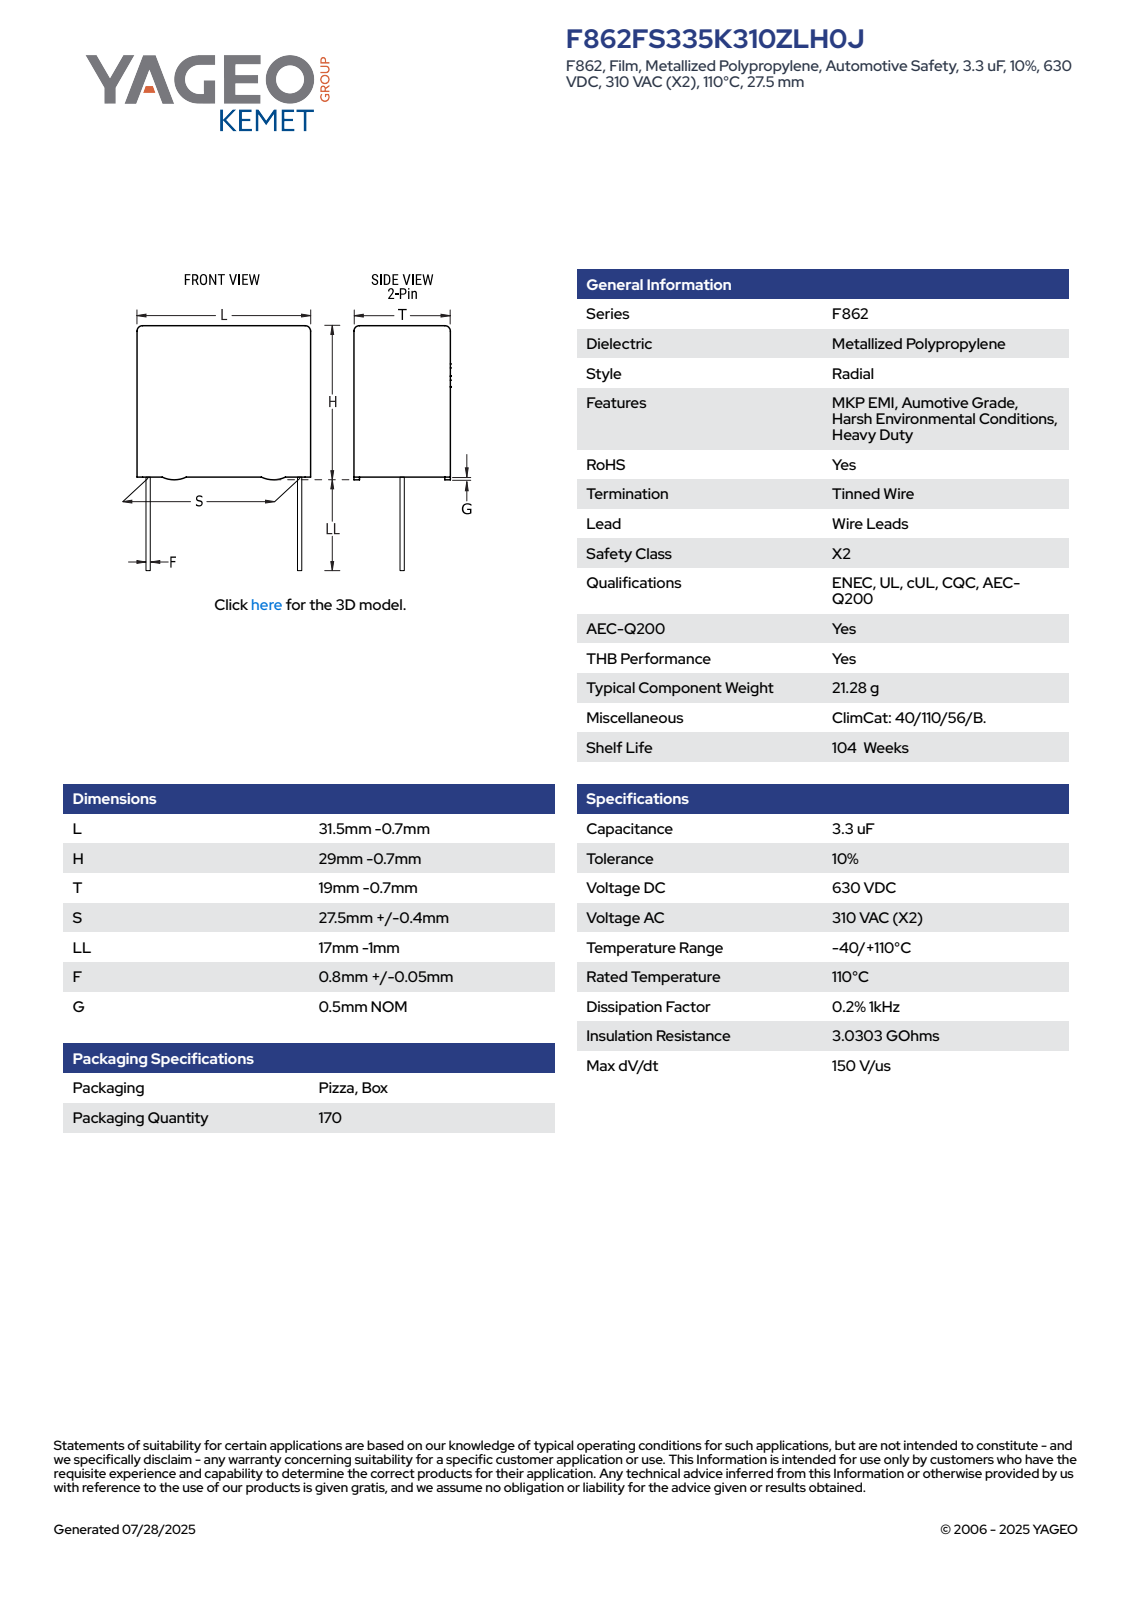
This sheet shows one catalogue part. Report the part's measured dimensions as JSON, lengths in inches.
{"part_name": "CFR_RBG_31.5X29X19_L30.8H28.3T18.3S27.5LL16F0.85G0.5", "step_written_by": "SolidWorks 2014 (AUTOMOTIVE_DESIGN)", "units": "inches", "bodies": {"solids": 4, "faces": 89, "planar": 81, "cylindrical": 8, "other": 0}, "overall_size": [1.744, 1.213, 0.72], "volume_in3": 0.958, "surface_area_in2": 6.276, "round_bosses_or_shafts": [[0.033, 2]], "partial_cylinders_radius": [[0.02, 4]], "face_to_face_distances": [0.72, 1.094, 1.213, 0.721, 0.02, 1.114, 0.041, 0.68, 0.041, 0.639]}
